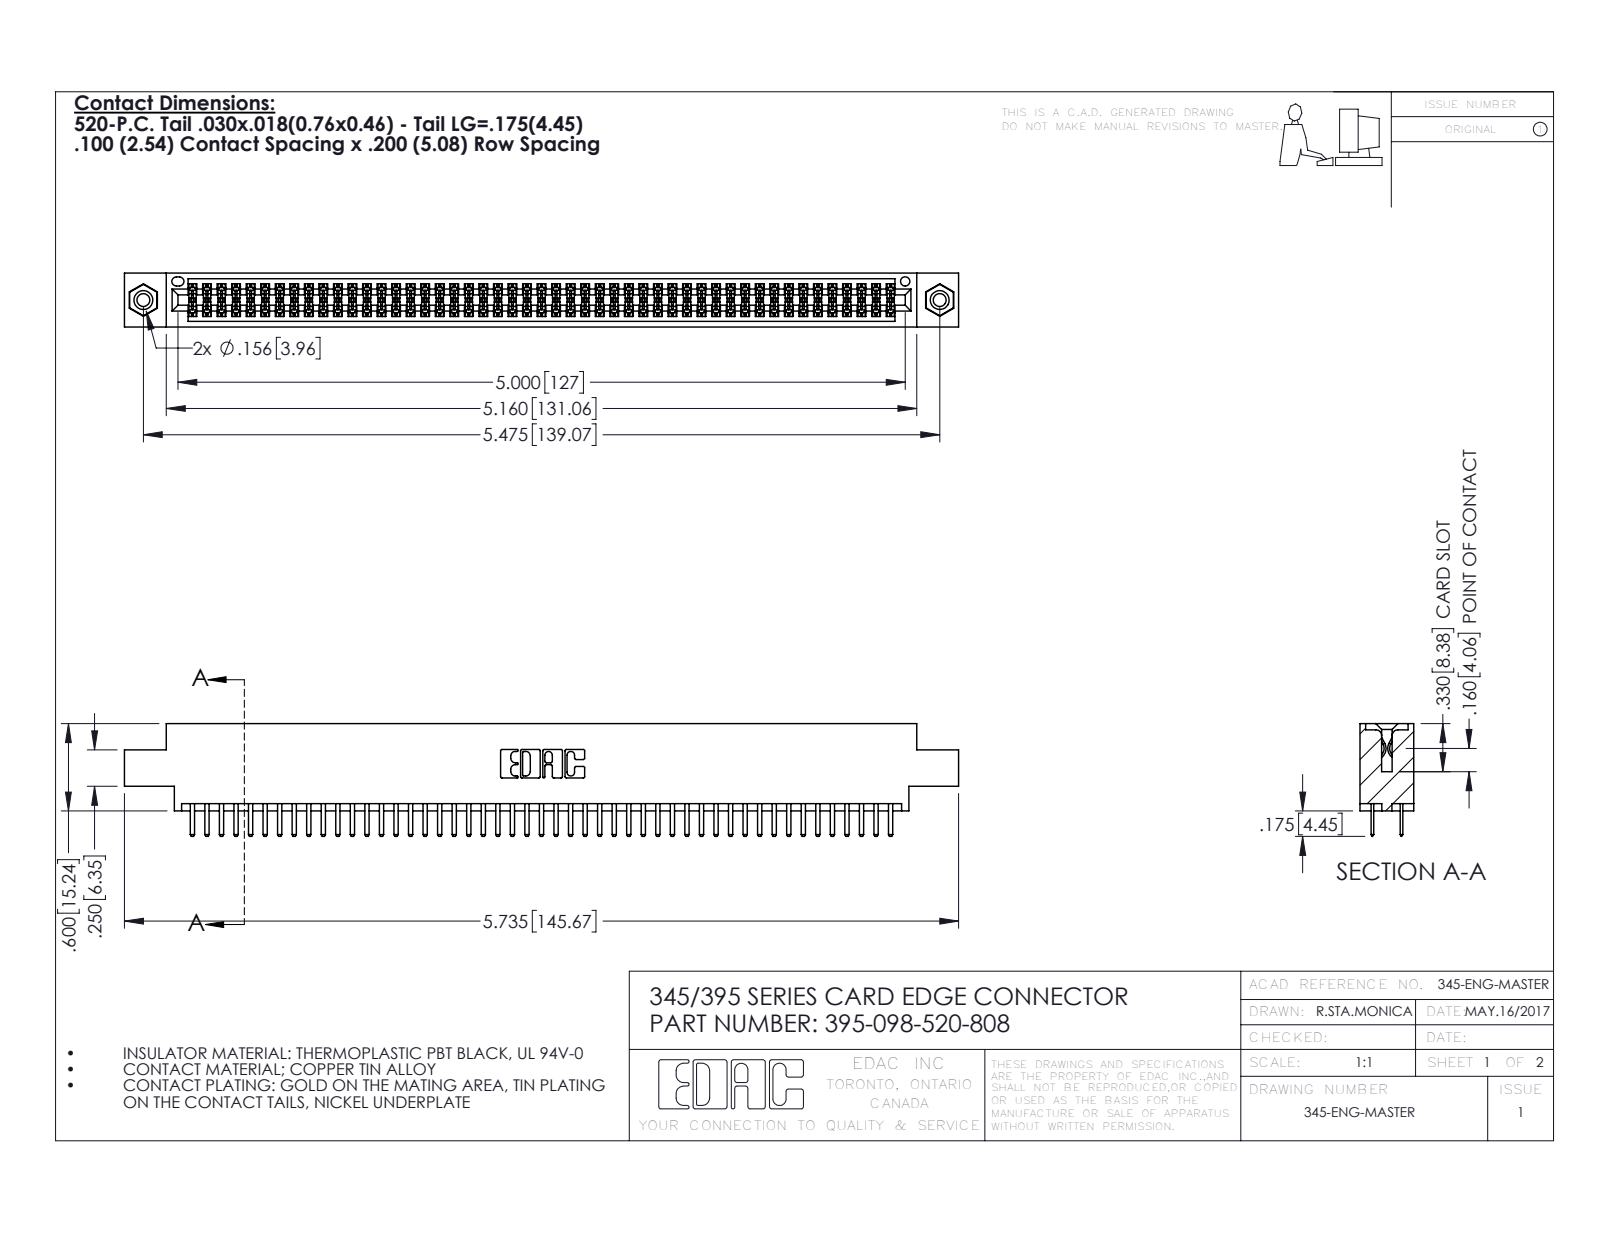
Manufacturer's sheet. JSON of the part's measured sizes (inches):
{"part_name": "345-250-001_345-250-003-102; 345 Part_0.170 Offset - 0.156 Dia-TI; 345-292-001_345-293-120; 395-098-520-808", "step_written_by": "SolidWorks 2016 (CONFIG_CONTROL_DESIGN)", "units": "inches", "bodies": {"solids": 101, "faces": 5482, "planar": 3546, "cylindrical": 1920, "other": 16}, "overall_size": [5.735, 0.775, 0.37], "volume_in3": 0.858, "surface_area_in2": 32.51, "round_holes": [[0.089, 2], [0.125, 2], [0.156, 2], [0.064, 1]], "round_bosses_or_shafts": [[0.155, 2]], "partial_cylinders_radius": [[0.006, 147], [0.01, 102], [0.01, 22], [0.007, 6], [0.031, 6], [0.026, 3], [0.014, 2], [0.019, 2]], "face_to_face_distances": [0.072, 0.298, 0.2, 0.37, 0.098, 0.272, 0.025, 0.225, 0.022, 0.072], "hole_center_spacings": [0.27, 5.239, 5.475]}
